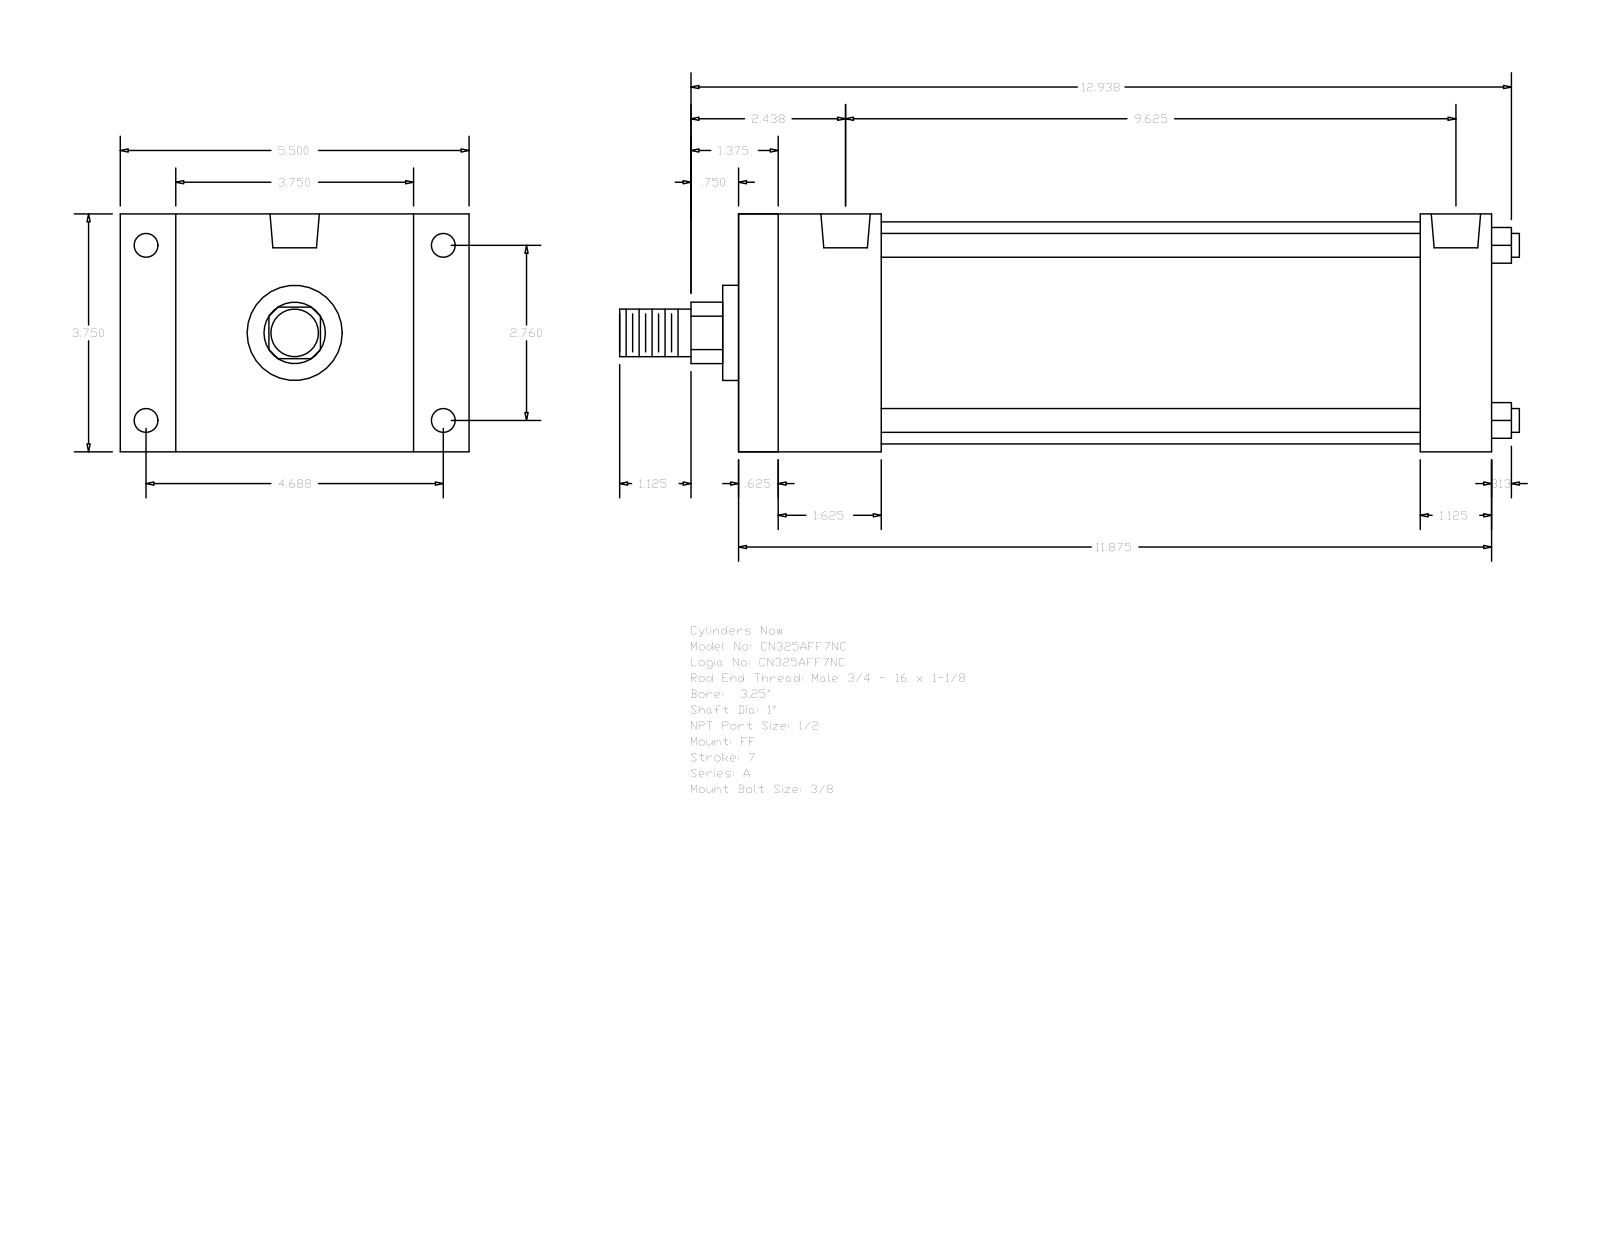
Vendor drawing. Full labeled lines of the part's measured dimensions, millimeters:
Part name (STEP PRODUCT): A_FF__0325_1
STEP written by: GSSL Pune (CONFIG_CONTROL_DESIGN)
Units: millimetres
Bodies: 0 solids, 92 faces (64 planar, 28 cylindrical, 0 other)
Overall size (bounding box): 360.36 × 139.7 × 95.25
Round holes (diameter × count): ⌀8.73 ×4, ⌀9.53 ×4, ⌀19.77 ×2
Round bosses / shafts (diameter × count): ⌀9.53 ×4, ⌀88.9 ×1, ⌀38.1 ×1, ⌀25.4 ×1, ⌀19.05 ×1
Partial cylindrical surfaces — rounded edges, fillets, slot ends (radius × count): R12.29 ×1
Main face-to-face distances: 95.24, 301.63, 15.87, 285.76, 22.23, 117.47, 57.15, 273.05, 41.28, 257.18
Hole centre spacings: 3.18, 70.1, 119.06, 138.16, 238.12, 241.3, 244.48
